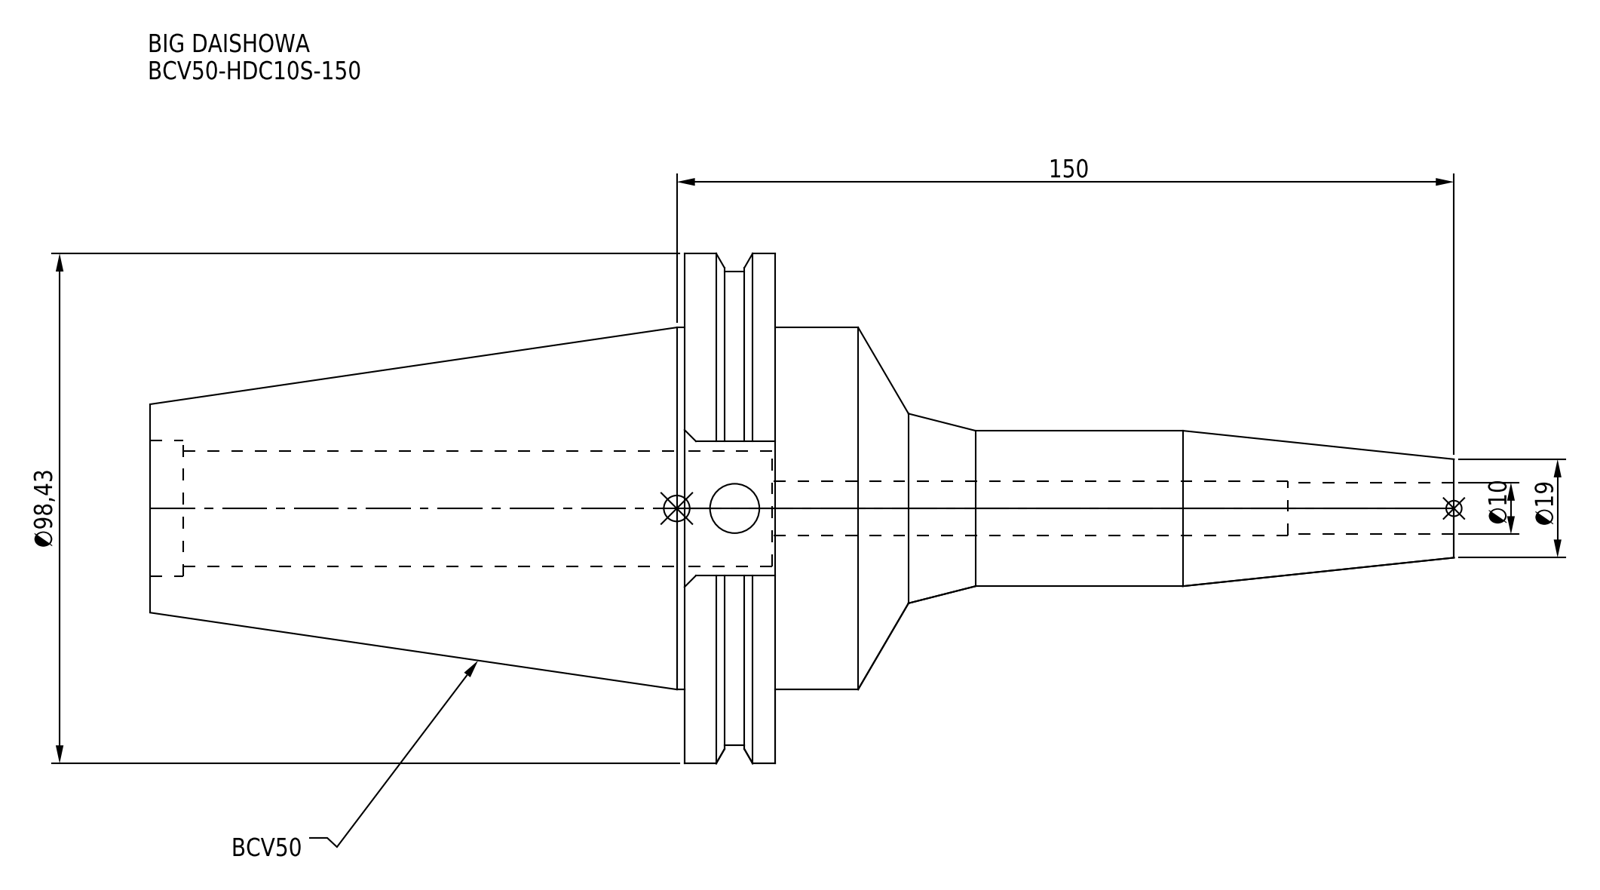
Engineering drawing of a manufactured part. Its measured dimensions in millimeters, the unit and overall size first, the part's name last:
Units: millimetres
Overall size (bounding box): 251.6 × 98.42 × 94.95
Round holes (diameter × count): ⌀9.53 ×1, ⌀10 ×1, ⌀10.5 ×1, ⌀22.3 ×1, ⌀26.23 ×1
Round bosses / shafts (diameter × count): ⌀98.42 ×1, ⌀91.29 ×1, ⌀69.85 ×1, ⌀30 ×1
Main face-to-face distances: 17.55, 120.65, 103.1, 72.95, 0.65, 16.9, 120, 25.92, 130.95, 131.6
Volume: 460 274 mm³ · Surface area: 61 604 mm²
Bodies: 1 solid, 58 faces (22 planar, 24 cylindrical, 12 other)
Part name (STEP PRODUCT): BCV50-HDC10S-150
STEP written by: CREO PARAMETRIC BY PTC INC, 2016380 (AUTOMOTIVE_DESIGN)
